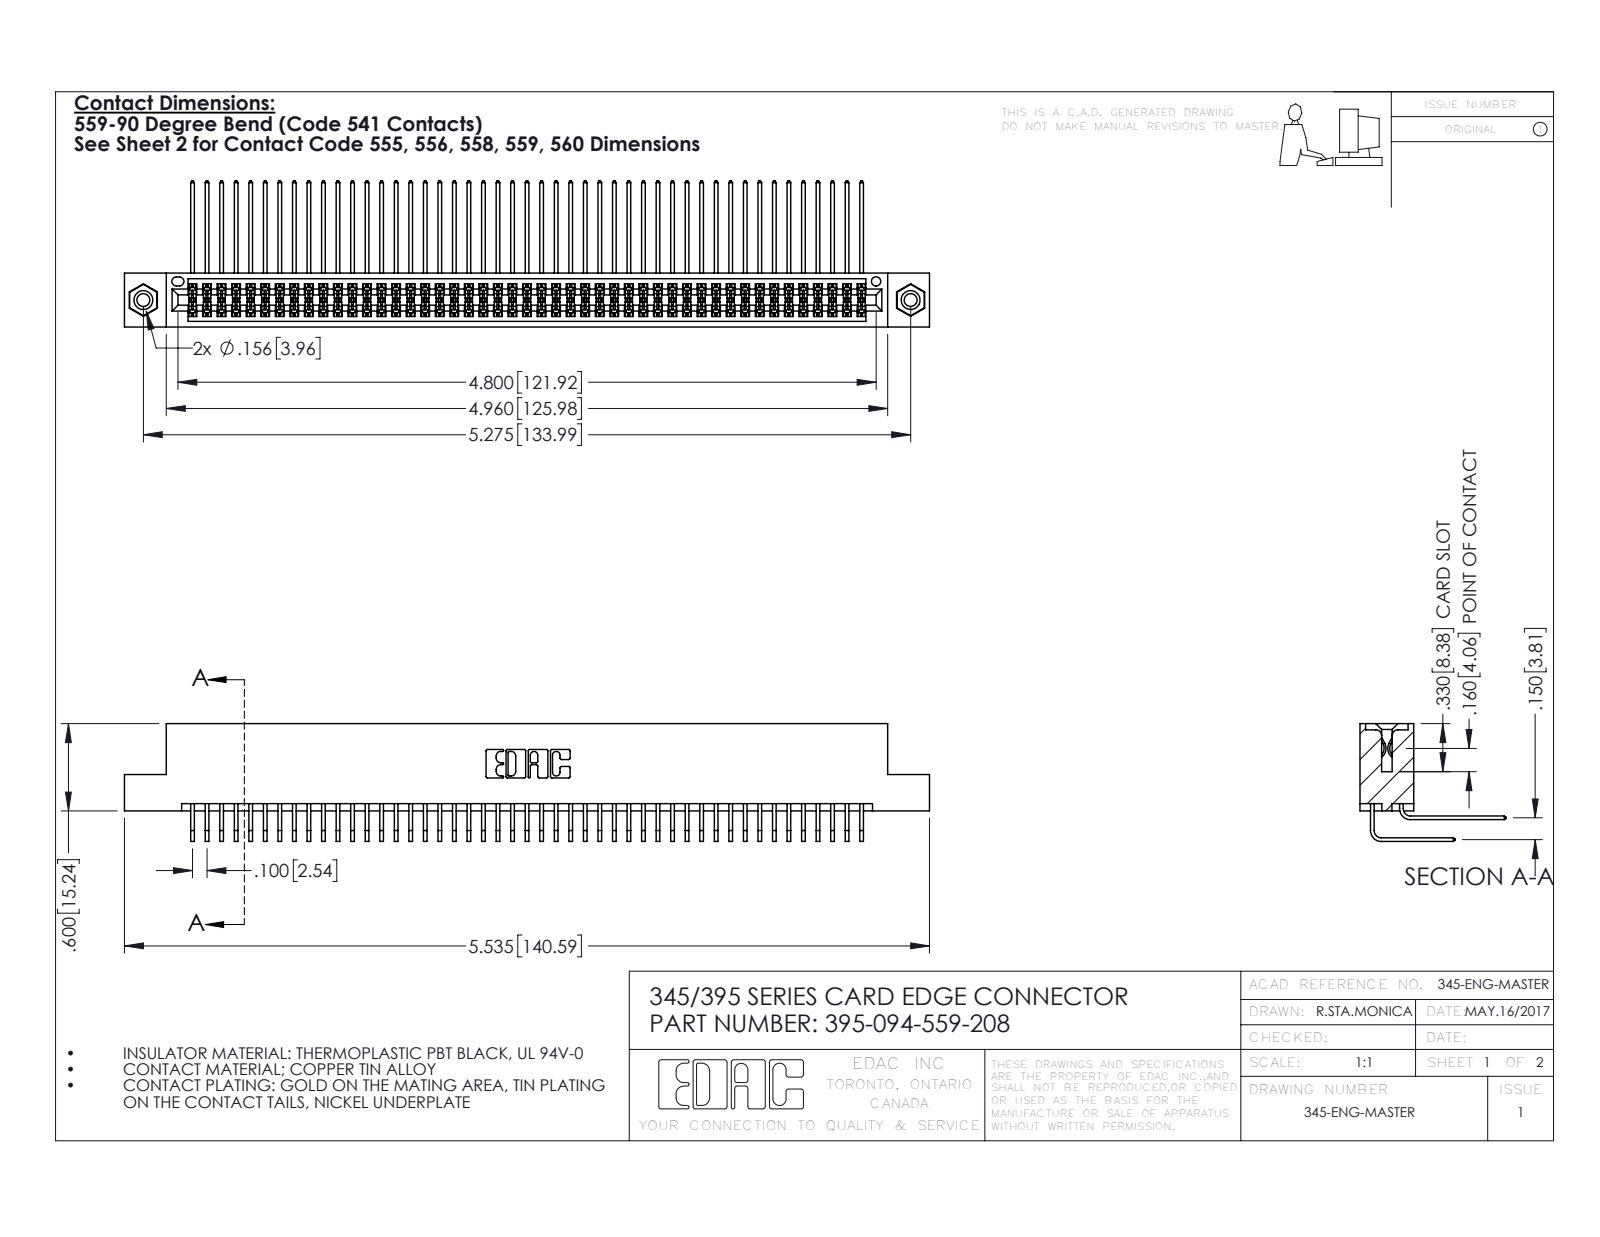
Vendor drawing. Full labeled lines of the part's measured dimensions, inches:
Part name (STEP PRODUCT): 345-292-001_558 559 Tail - 1; 345 Part_Flush Mounting Lugs - 0.156 Dia-TI; 395-094-559-208; 345-250-001_345-250-003-102 (+1 more)
STEP written by: SolidWorks 2016 (CONFIG_CONTROL_DESIGN)
Units: inches
Bodies: 97 solids, 5074 faces (3402 planar, 1656 cylindrical, 16 other)
Overall size (bounding box): 5.535 × 1.005 × 0.809
Volume: 0.869 in³ · Surface area: 36.75 in²
Round holes (diameter × count): ⌀0.089 ×2, ⌀0.125 ×2, ⌀0.156 ×2, ⌀0.064 ×1
Round bosses / shafts (diameter × count): ⌀0.155 ×2
Partial cylindrical surfaces — rounded edges, fillets, slot ends (radius × count): R0.006 ×141, R0.01 ×22, R0.007 ×6, R0.031 ×6, R0.026 ×3, R0.014 ×2, R0.019 ×2, R0.022 ×2
Main face-to-face distances: 0.072, 0.298, 0.2, 0.37, 0.098, 0.272, 0.025, 0.225, 0.175, 0.15
Hole centre spacings: 0.27, 5.039, 5.275
